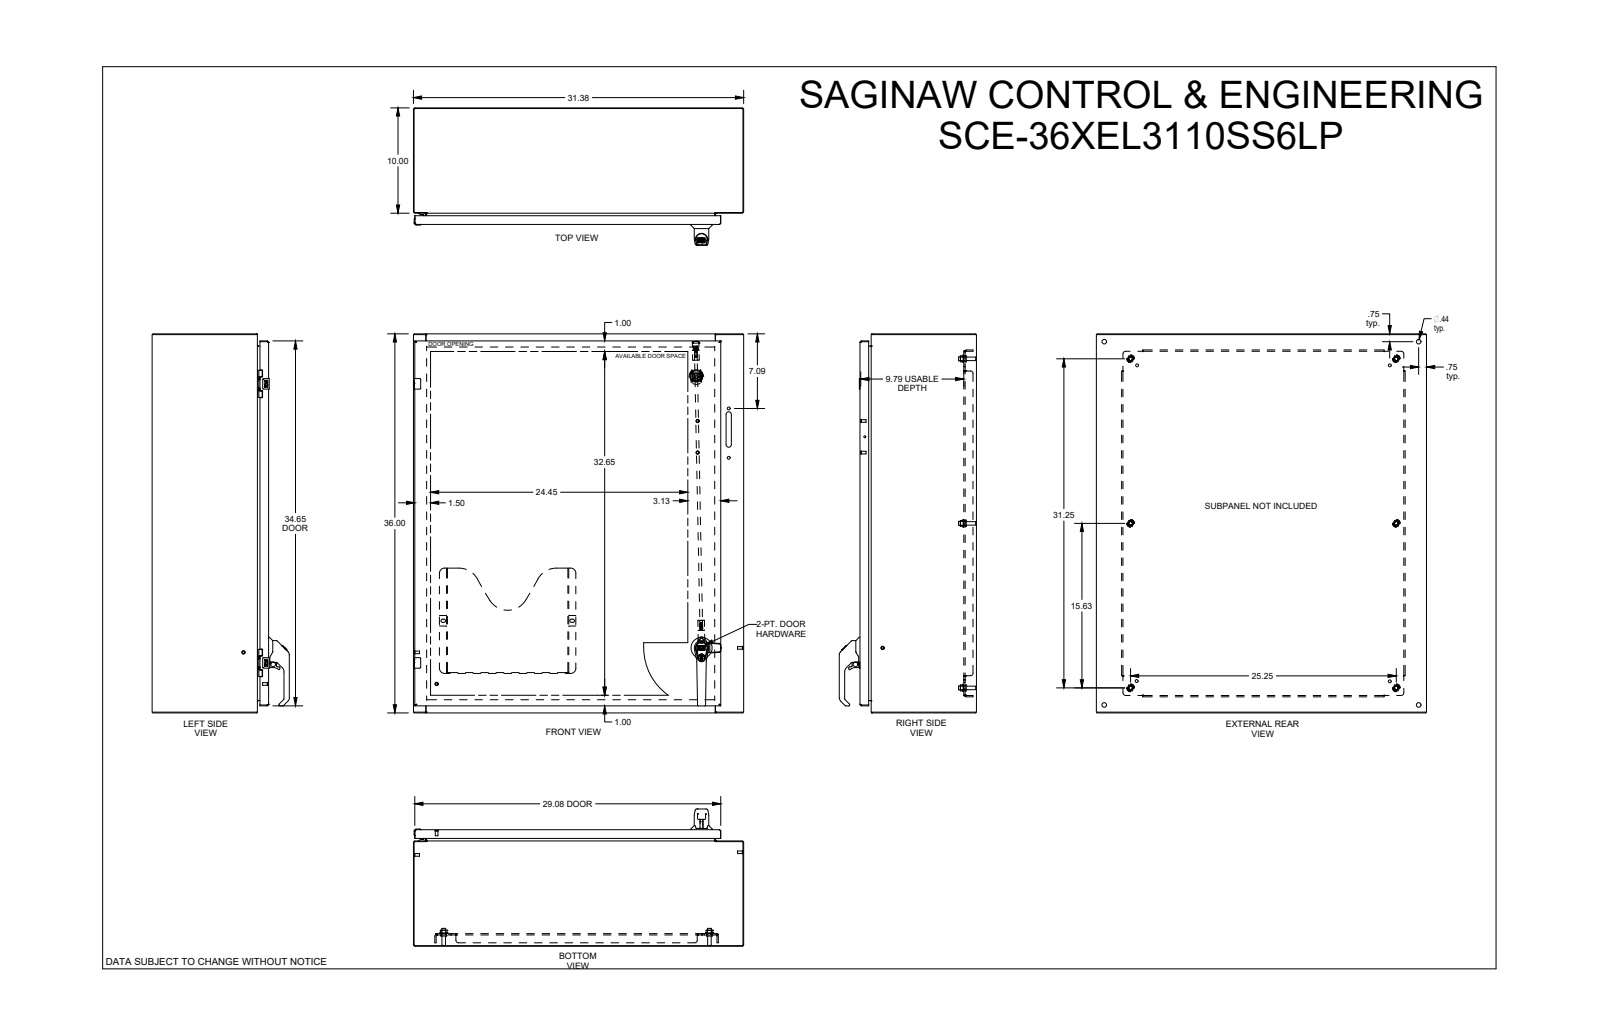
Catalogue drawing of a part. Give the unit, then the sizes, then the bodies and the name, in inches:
Units: inches
Overall size (bounding box): 36 × 31.375 × 13.036
Round holes (diameter × count): ⌀0.281 ×6, ⌀0.367 ×6, ⌀0.5 ×6, ⌀0.266 ×5, ⌀0.172 ×4, ⌀0.205 ×4, ⌀0.244 ×4, ⌀0.375 ×4, ⌀0.437 ×4, ⌀0.25 ×3, ⌀0.25 ×3, ⌀0.138 ×2
Round bosses / shafts (diameter × count): ⌀0.248 ×8, ⌀0.366 ×6, ⌀0.332 ×6, ⌀0.17 ×6, ⌀0.25 ×4, ⌀0.563 ×3, ⌀0.196 ×3, ⌀0.341 ×2
Partial cylindrical surfaces — rounded edges, fillets, slot ends (radius × count): R0.03 ×69, R0.015 ×54, R0.01 ×48, R0.02 ×36, R0.02 ×34, R0.04 ×31, R0.039 ×30, R0.005 ×26
Main face-to-face distances: 0.075, 10.993, 0.075, 10.918, 11.068, 1.125, 1.2, 9.868, 9.793, 0.125
Hole centre spacings: 26.5, 0.985, 0.02, 4.493, 26.542, 26.562, 0.472, 0.725
Volume: 453.2 in³ · Surface area: 10 369 in²
Bodies: 71 solids, 4738 faces (1767 planar, 1238 cylindrical, 1733 other)
Part name (STEP PRODUCT): SCE-36XEL3110SS6LP
STEP written by: SolidWorks 2019 (CONFIG_CONTROL_DESIGN)
